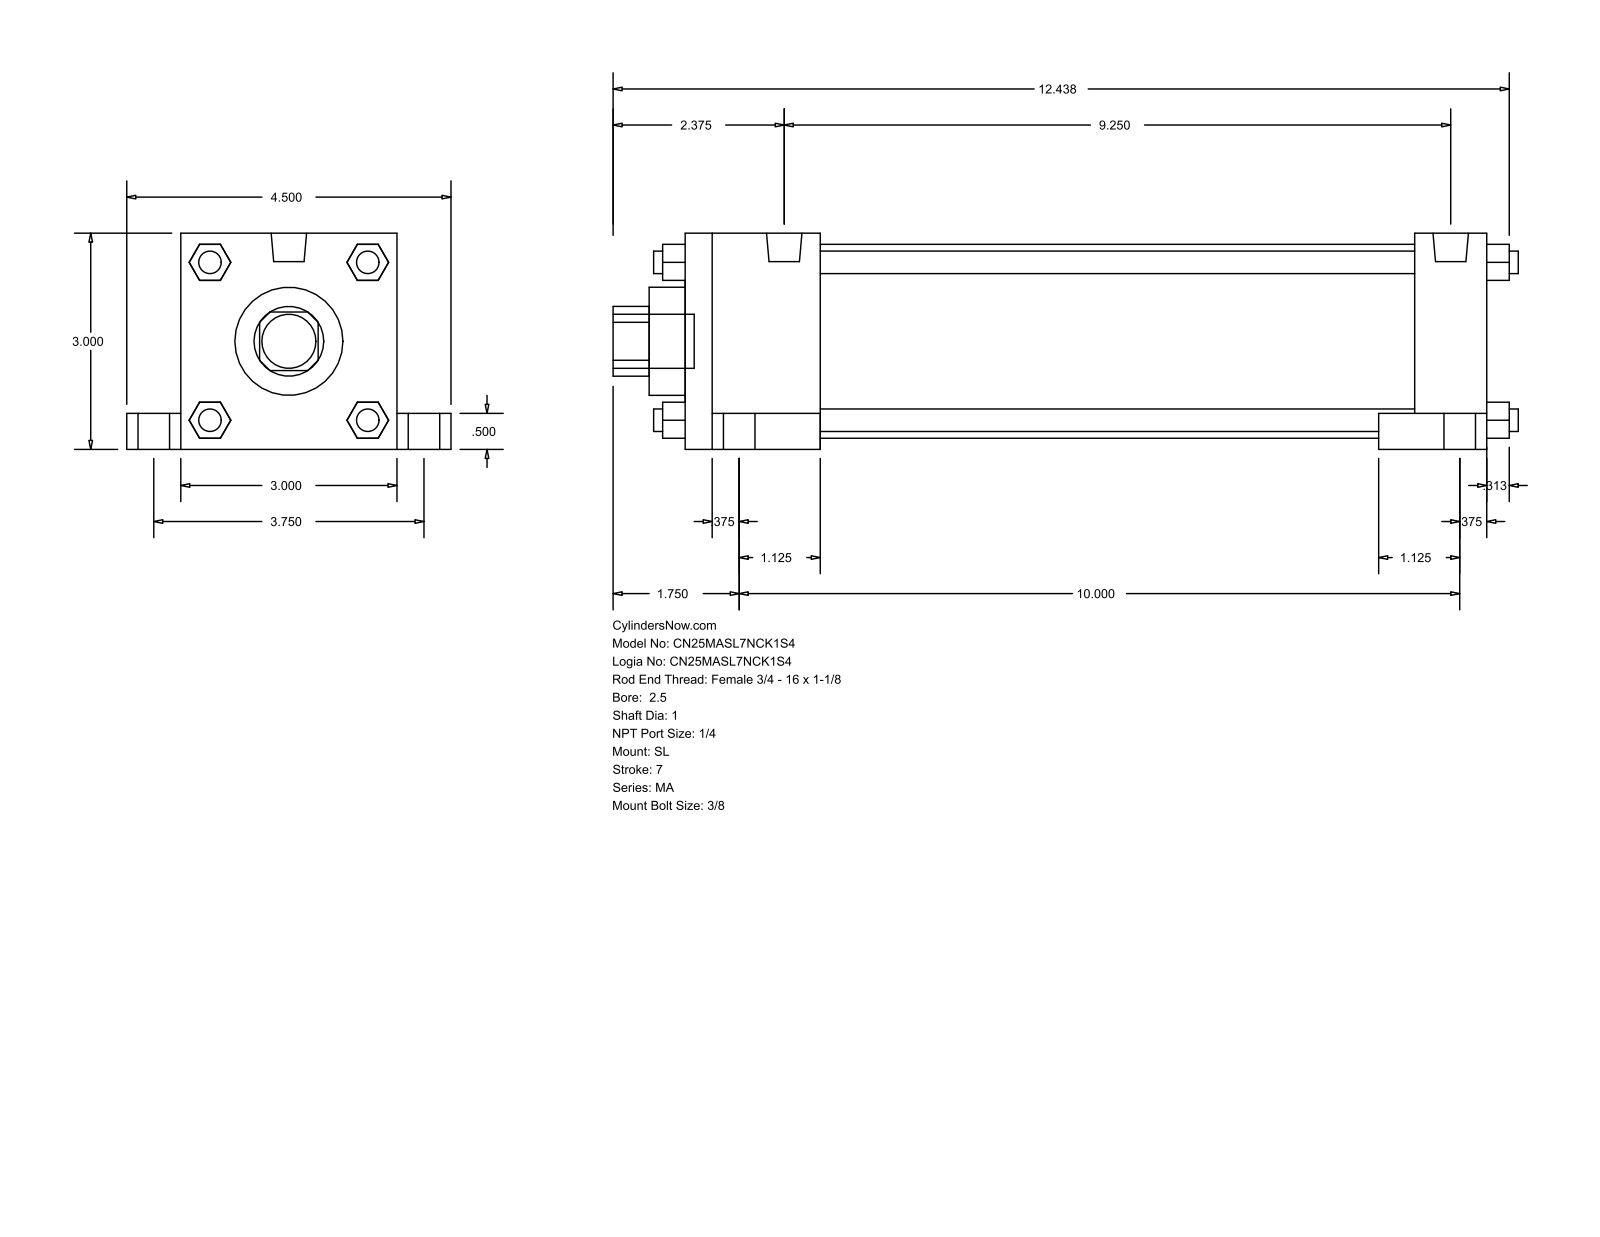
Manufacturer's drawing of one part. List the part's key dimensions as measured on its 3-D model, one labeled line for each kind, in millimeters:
Part name (STEP PRODUCT): MA_SL__0250_1
STEP written by: GSSL Pune (CONFIG_CONTROL_DESIGN)
Units: millimetres
Bodies: 0 solids, 148 faces (112 planar, 36 cylindrical, 0 other)
Overall size (bounding box): 319.09 × 114.3 × 76.2
Round holes (diameter × count): ⌀25.4 ×1, ⌀38.1 ×1, ⌀68.33 ×1
Round bosses / shafts (diameter × count): ⌀7.94 ×8, ⌀17.46 ×4, ⌀11.11 ×4, ⌀12.49 ×2, ⌀19.05 ×1
Partial cylindrical surfaces — rounded edges, fillets, slot ends (radius × count): R12.29 ×1
Main face-to-face distances: 76.2, 282.58, 12.7, 47.63, 234.95, 257.17, 209.54, 25.41, 19.05, 95.25
